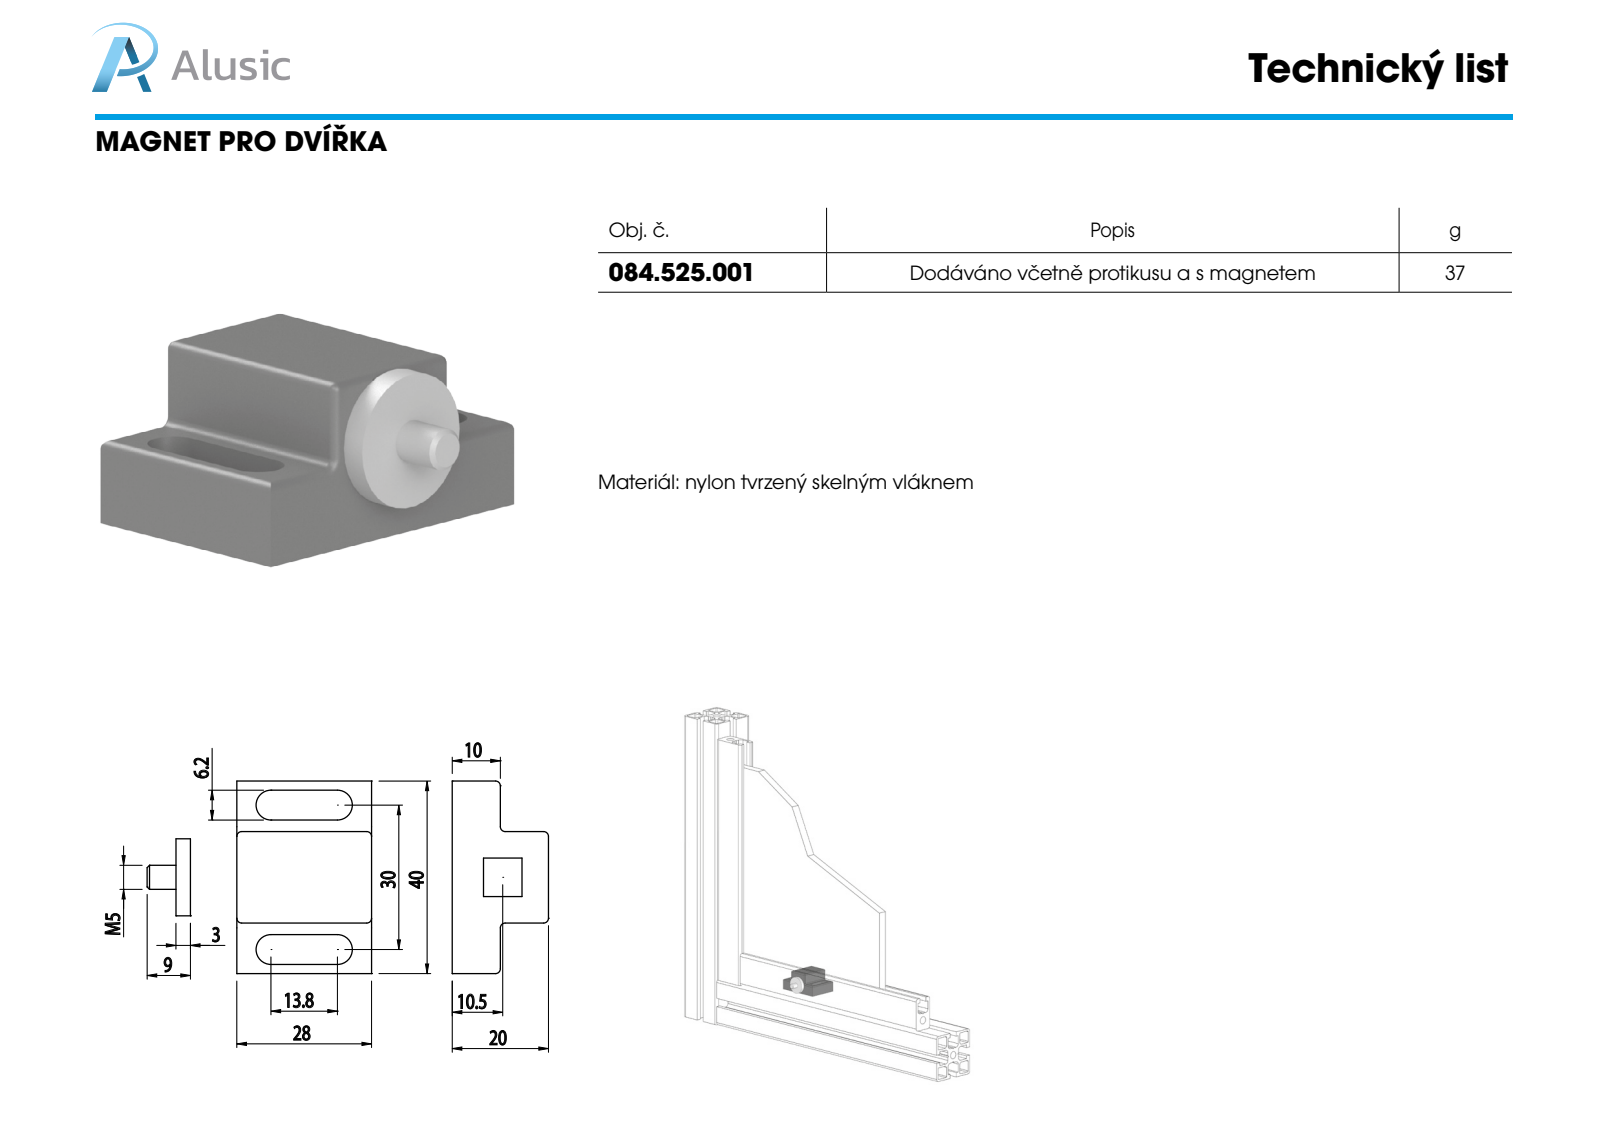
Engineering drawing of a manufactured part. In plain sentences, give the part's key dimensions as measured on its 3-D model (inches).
The part is named "084.525.001". Its 3-D file was written by "SolidWorks 2011 (CONFIG_CONTROL_DESIGN)". It is 2 solids with 51 faces: 17 planar, 24 cylindrical and 10 other. Overall it measures 1.575 by 1.457 by 0.787 inches. Its volume is 0.908 cubic inches and its surface area 8.584 square inches. Round bosses or shafts: 1 of diameter 0.63, 1 of diameter 0.197. Partial cylindrical surfaces (rounded edges, fillets, slot ends): 14 of radius 0.039, 4 of radius 0.122. The main face-to-face distances are 1.102, 0.787, 0.394, 0.413, 1.161, 0.319, 1.256, 0.094, 0.843, 0.075.
